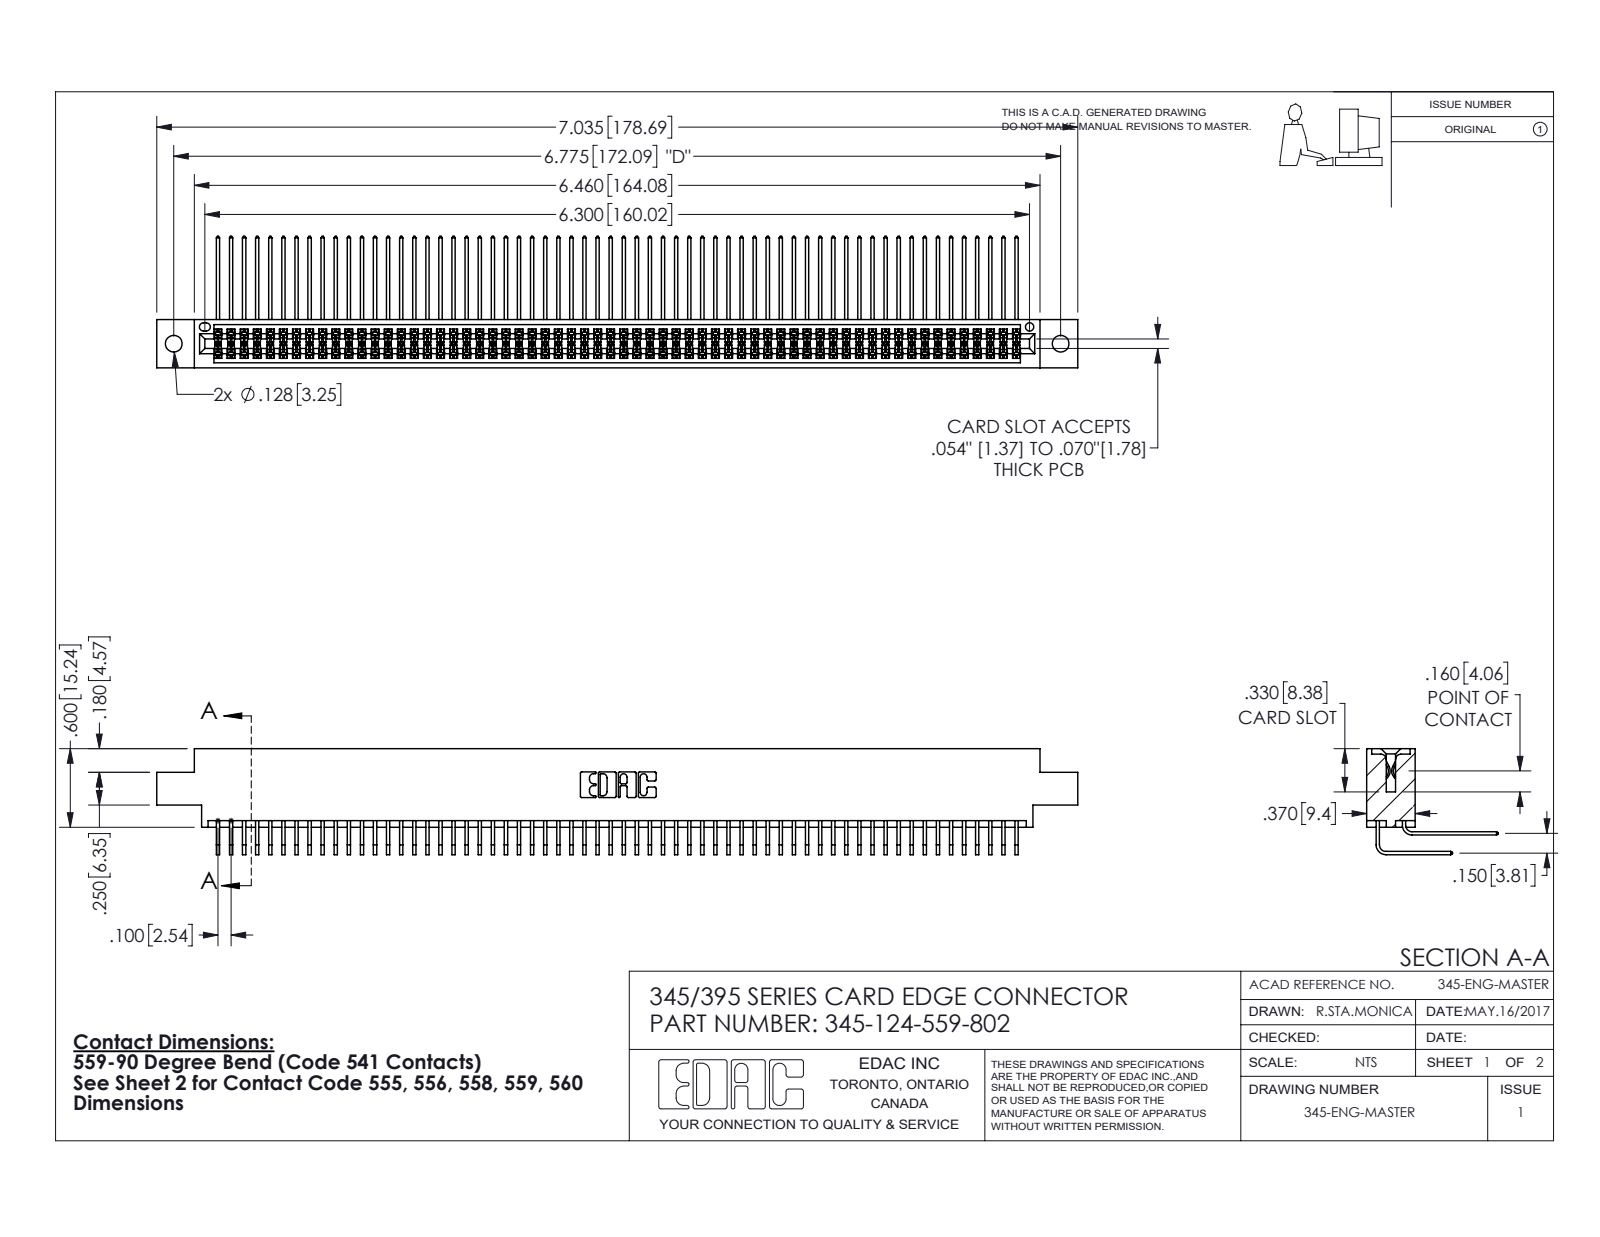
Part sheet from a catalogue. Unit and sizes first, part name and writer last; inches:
Units: inches
Overall size (bounding box): 7.035 × 1.005 × 0.809
Round holes (diameter × count): ⌀0.128 ×2, ⌀0.064 ×1
Partial cylindrical surfaces — rounded edges, fillets, slot ends (radius × count): R0.006 ×247, R0.01 ×22, R0.007 ×6, R0.031 ×6, R0.026 ×3, R0.014 ×2, R0.019 ×2, R0.022 ×2
Main face-to-face distances: 0.072, 0.298, 0.37, 0.2, 0.098, 0.272, 0.025, 0.225, 0.175, 0.15
Hole centre spacings: 0.27, 6.539, 6.775
Volume: 1.105 in³ · Surface area: 47.1 in²
Bodies: 125 solids, 6578 faces (4424 planar, 2154 cylindrical, 0 other)
Part name (STEP PRODUCT): 345-292-001_558 559 Tail - 1; 345-292-001_559 Tail - 2; 345 Part_0.170 Offset - 0.128 Dia; 345-124-559-802
STEP written by: SolidWorks 2016 (CONFIG_CONTROL_DESIGN)
